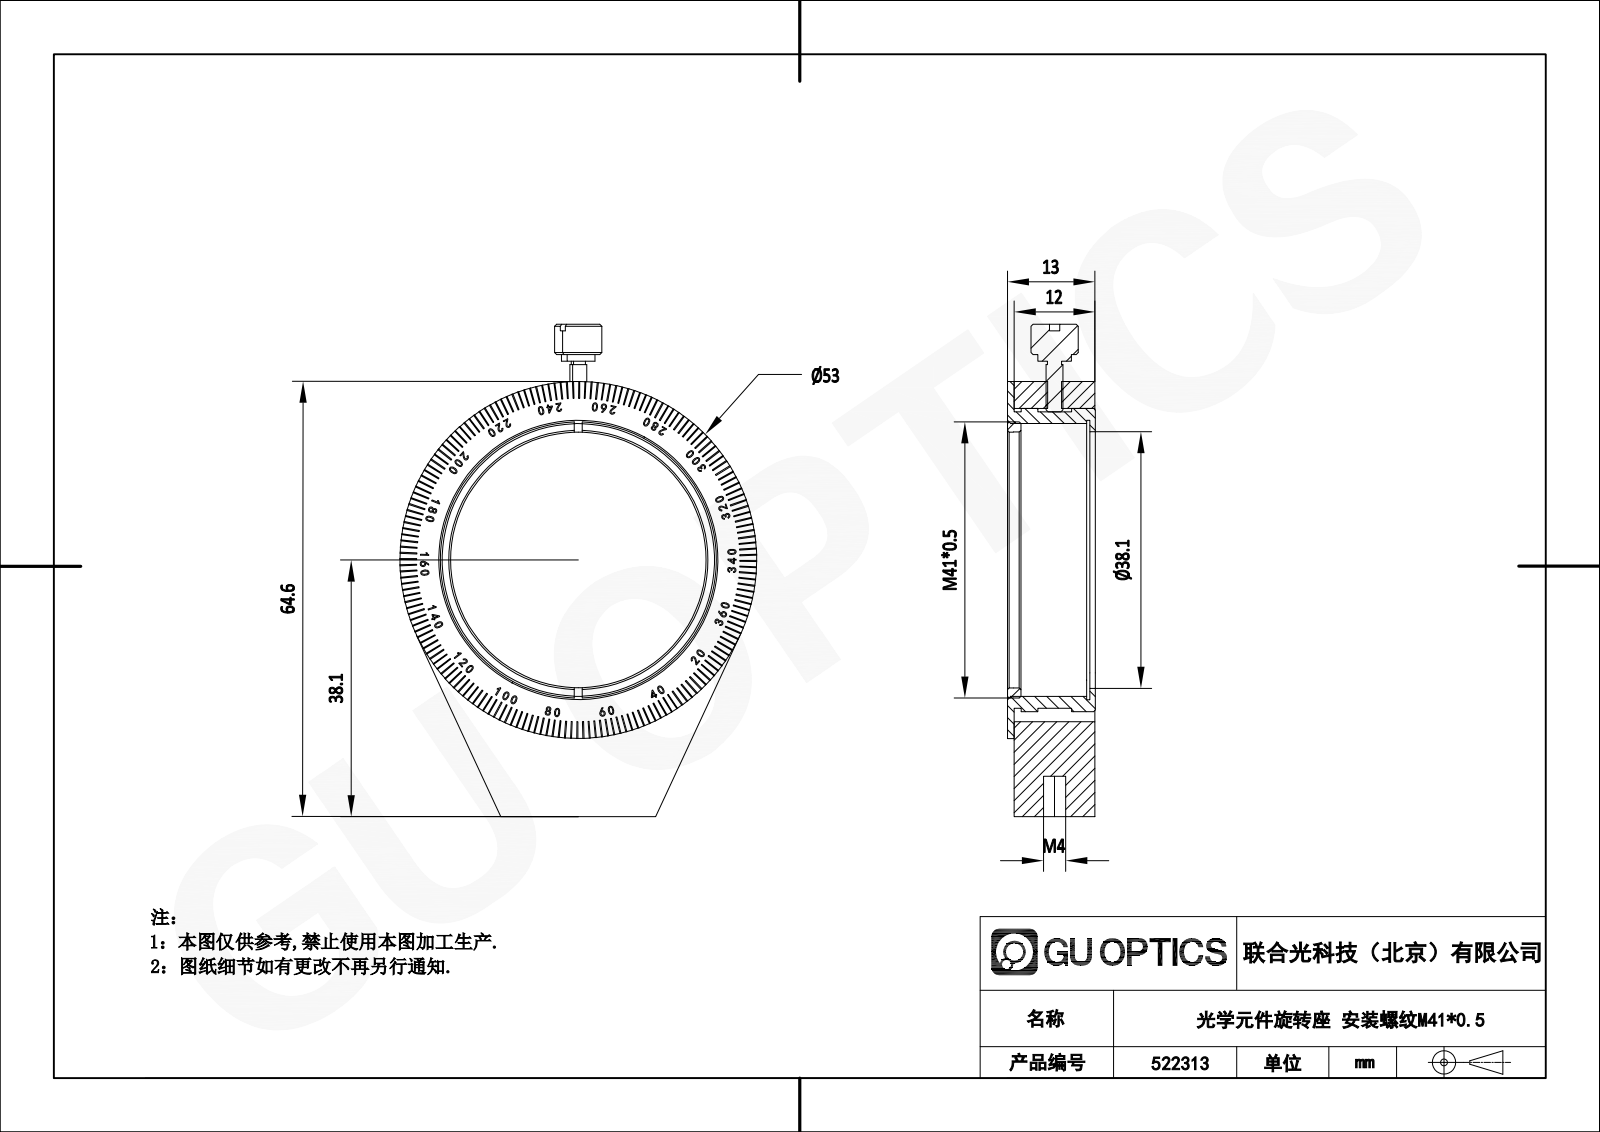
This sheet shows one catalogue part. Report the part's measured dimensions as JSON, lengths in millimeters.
{"part_name": "ZFK透镜卡环压圈_1.8.5.55_ZFK-K40", "step_written_by": "SolidWorks 2021 (CONFIG_CONTROL_DESIGN)", "units": "millimeters", "bodies": {"solids": 4, "faces": 1216, "planar": 987, "cylindrical": 37, "other": 192}, "overall_size": [73.1, 53, 13.05], "volume_mm3": 16835, "surface_area_mm2": 13243, "round_holes": [[2.05, 1], [3.3, 1], [38, 1], [38.1, 1], [40.5, 1], [41.5, 1]], "round_bosses_or_shafts": [[53, 1], [45, 1], [44, 1], [41, 1], [7, 1], [5, 1], [2.5, 1], [2.1, 1]], "partial_cylinders_radius": [[19, 1]], "face_to_face_distances": [1, 12, 13, 12.05, 13.05, 0.8, 0.75, 11.25, 12.25, 11]}
